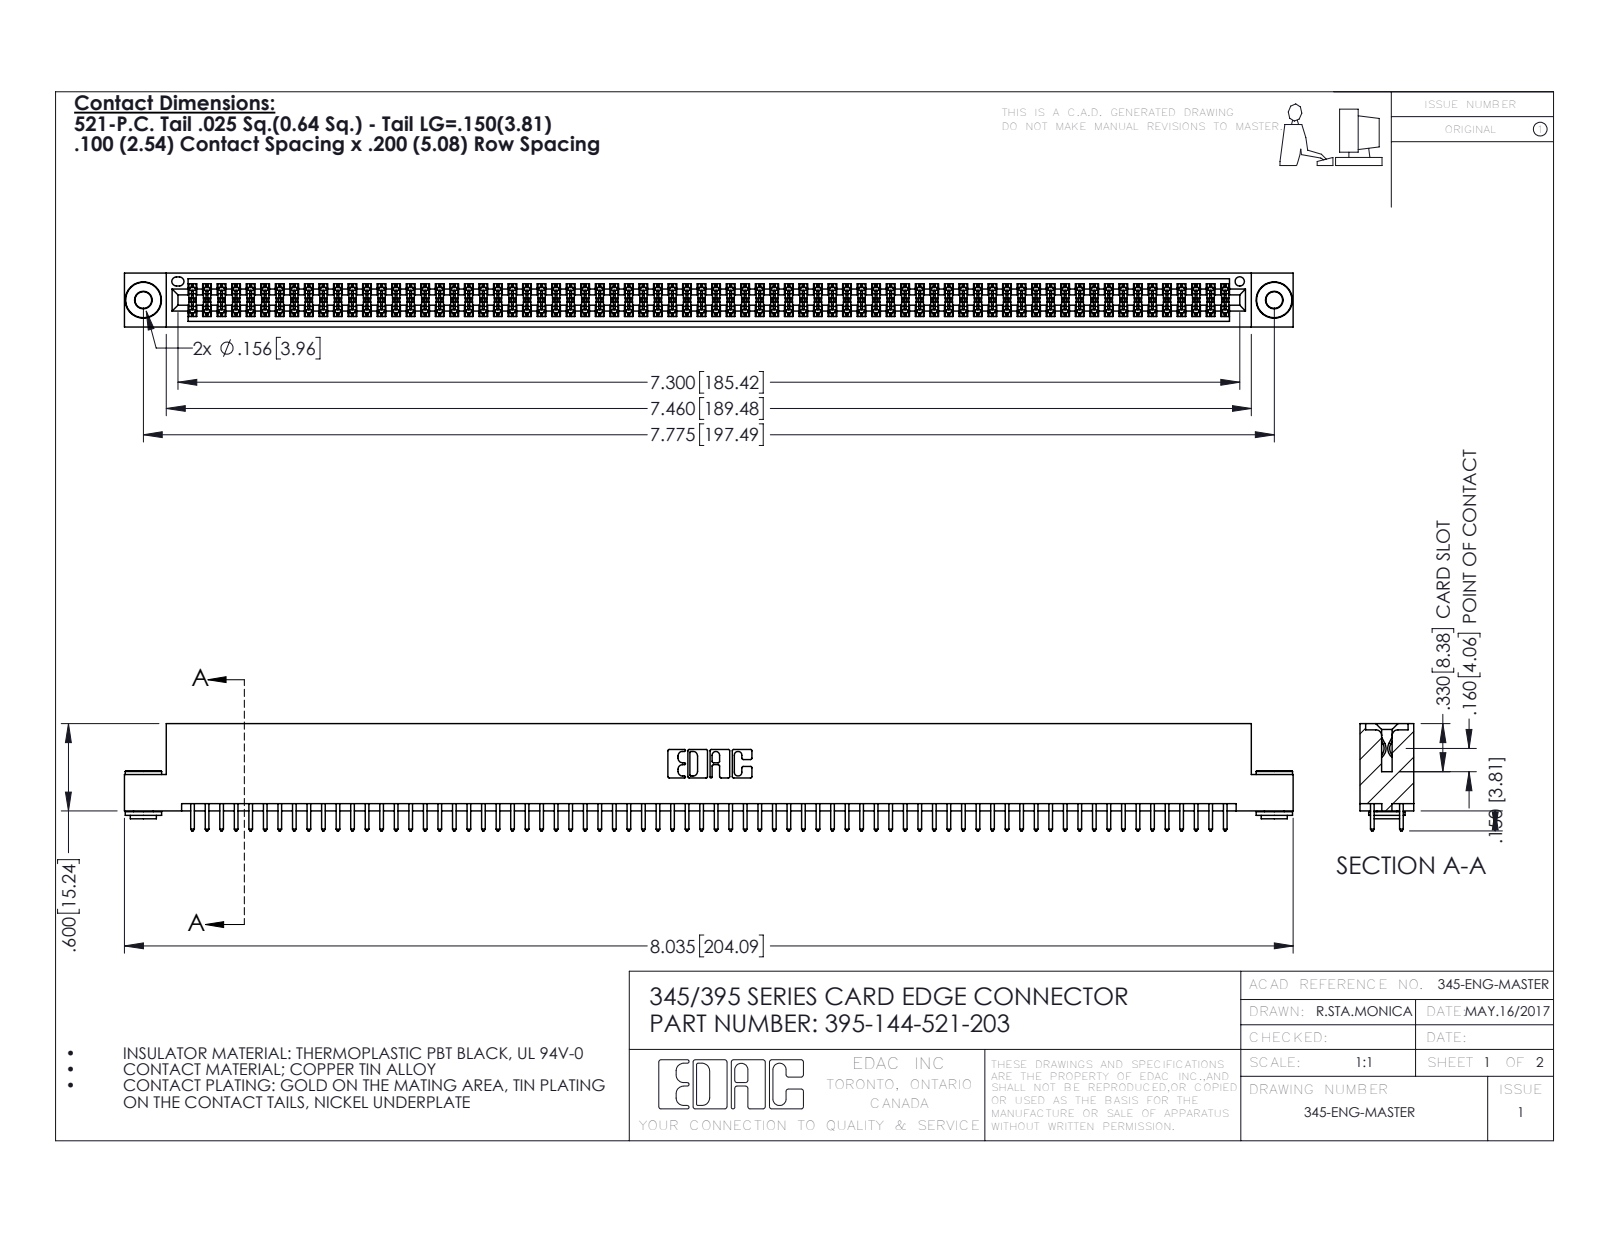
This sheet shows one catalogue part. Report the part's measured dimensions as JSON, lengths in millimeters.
{"part_name": "345 Part_Flush Mounting Lugs - 0.156 Dia-TH; 345-292-001_345-293-121; 395-144-521-203; 345-250-002_345-250-002-102", "step_written_by": "SolidWorks 2016 (CONFIG_CONTROL_DESIGN)", "units": "millimeters", "bodies": {"solids": 147, "faces": 7364, "planar": 4842, "cylindrical": 2514, "other": 8}, "overall_size": [204.1, 18.7, 9.4], "volume_mm3": 20060, "surface_area_mm2": 30060, "round_holes": [[2.9, 2], [4, 2], [1.6, 1]], "round_bosses_or_shafts": [[6.4, 2], [4.6, 2], [3.5, 2]], "partial_cylinders_radius": [[0.2, 216], [0.3, 144], [0.3, 22], [0.2, 6], [0.8, 6], [0.7, 3], [0.4, 2], [0.5, 2]], "face_to_face_distances": [1.8, 7.6, 5.1, 0.6, 2.5, 6.9, 9.4, 5.7, 4.4, 3.8], "hole_center_spacings": [6.9, 191.5, 197.5]}
